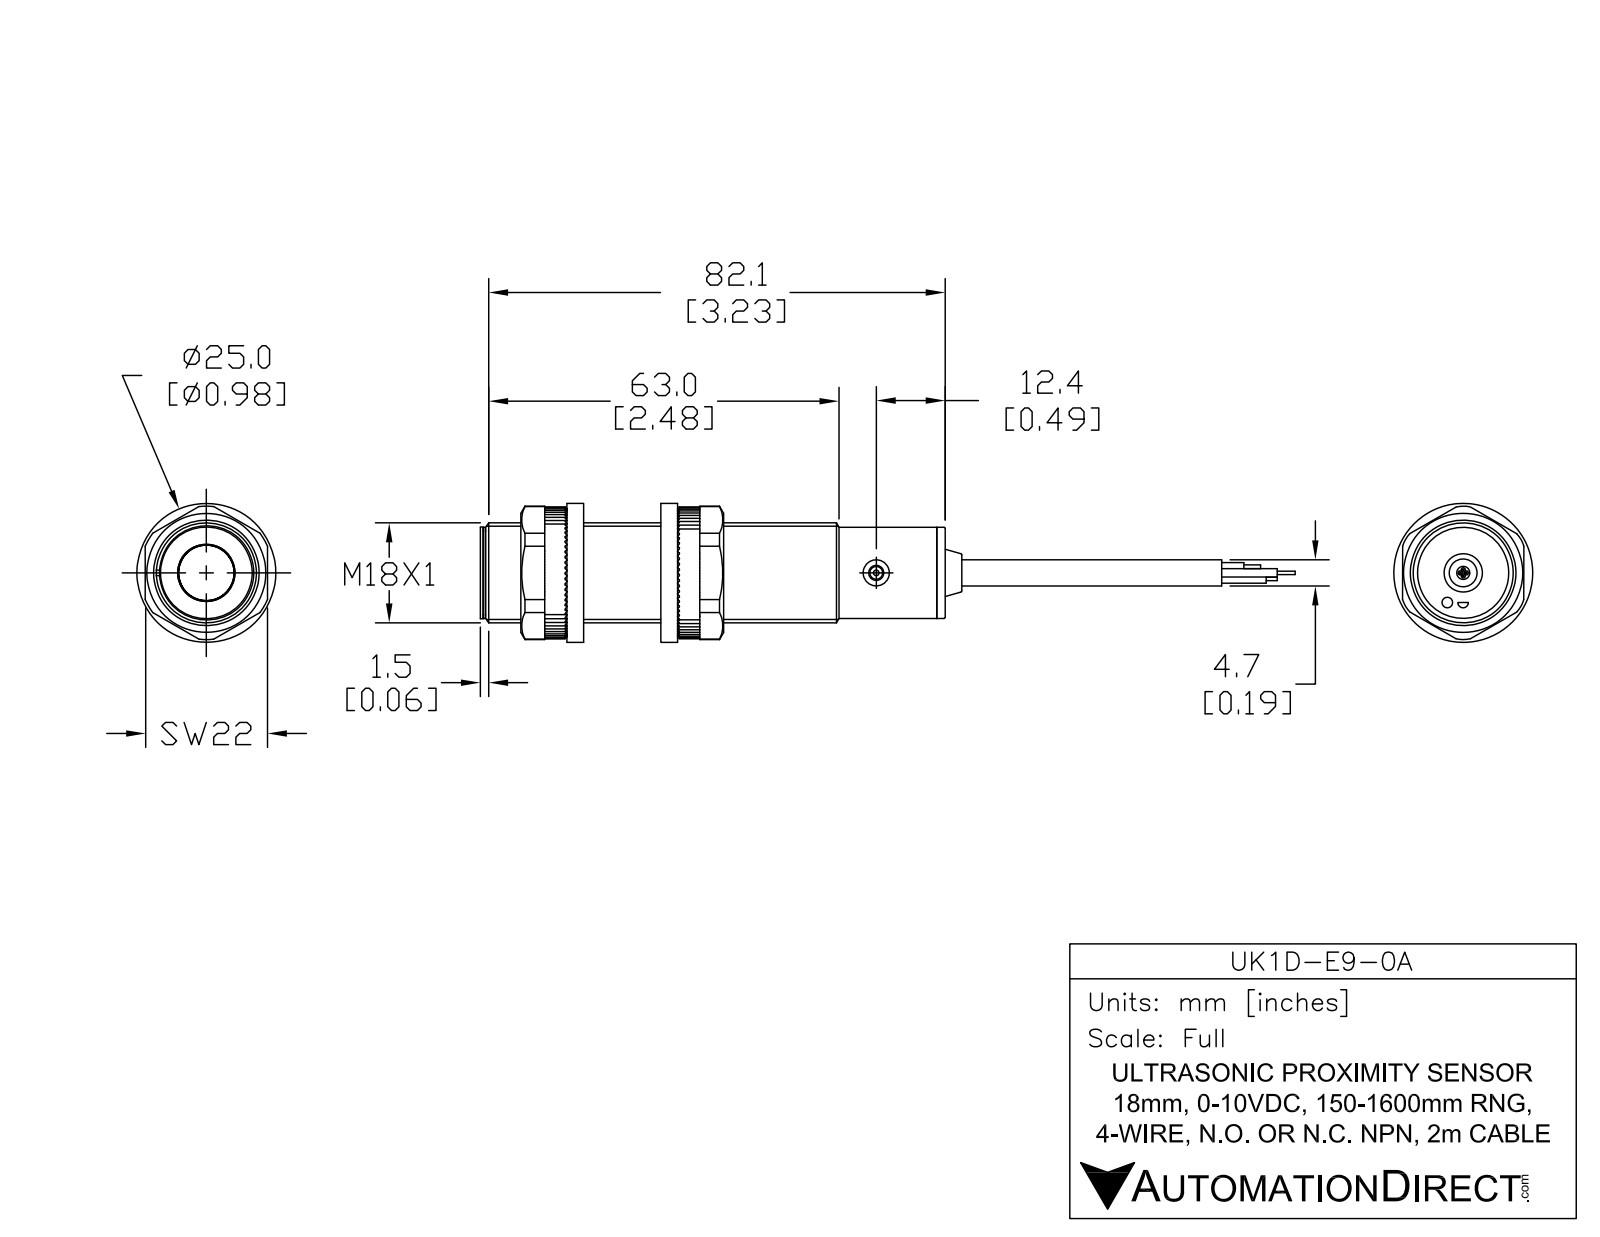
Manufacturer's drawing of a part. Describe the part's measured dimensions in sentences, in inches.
The part is named "UK1D-E9-0A". Its 3-D file was written by "SolidWorks 2017 (AUTOMOTIVE_DESIGN)". It is 6 solids with 55 faces: 17 planar, 24 cylindrical and 14 other. Overall it measures 4.832 by 0.709 by 0.709 inches. Its volume is 1.285 cubic inches and its surface area 10.69 square inches. Round holes: 2 of diameter 0.185, 1 of diameter 0.106. Round bosses or shafts: 1 of diameter 0.709, 1 of diameter 0.646, 1 of diameter 0.622, 1 of diameter 0.374, 1 of diameter 0.189, 1 of diameter 0.091. The main face-to-face distances are 3.193, 3.252, 0.059, 0.039, 3.232, 3.291, 0.041, 3.234, 3.293, 3.257.
